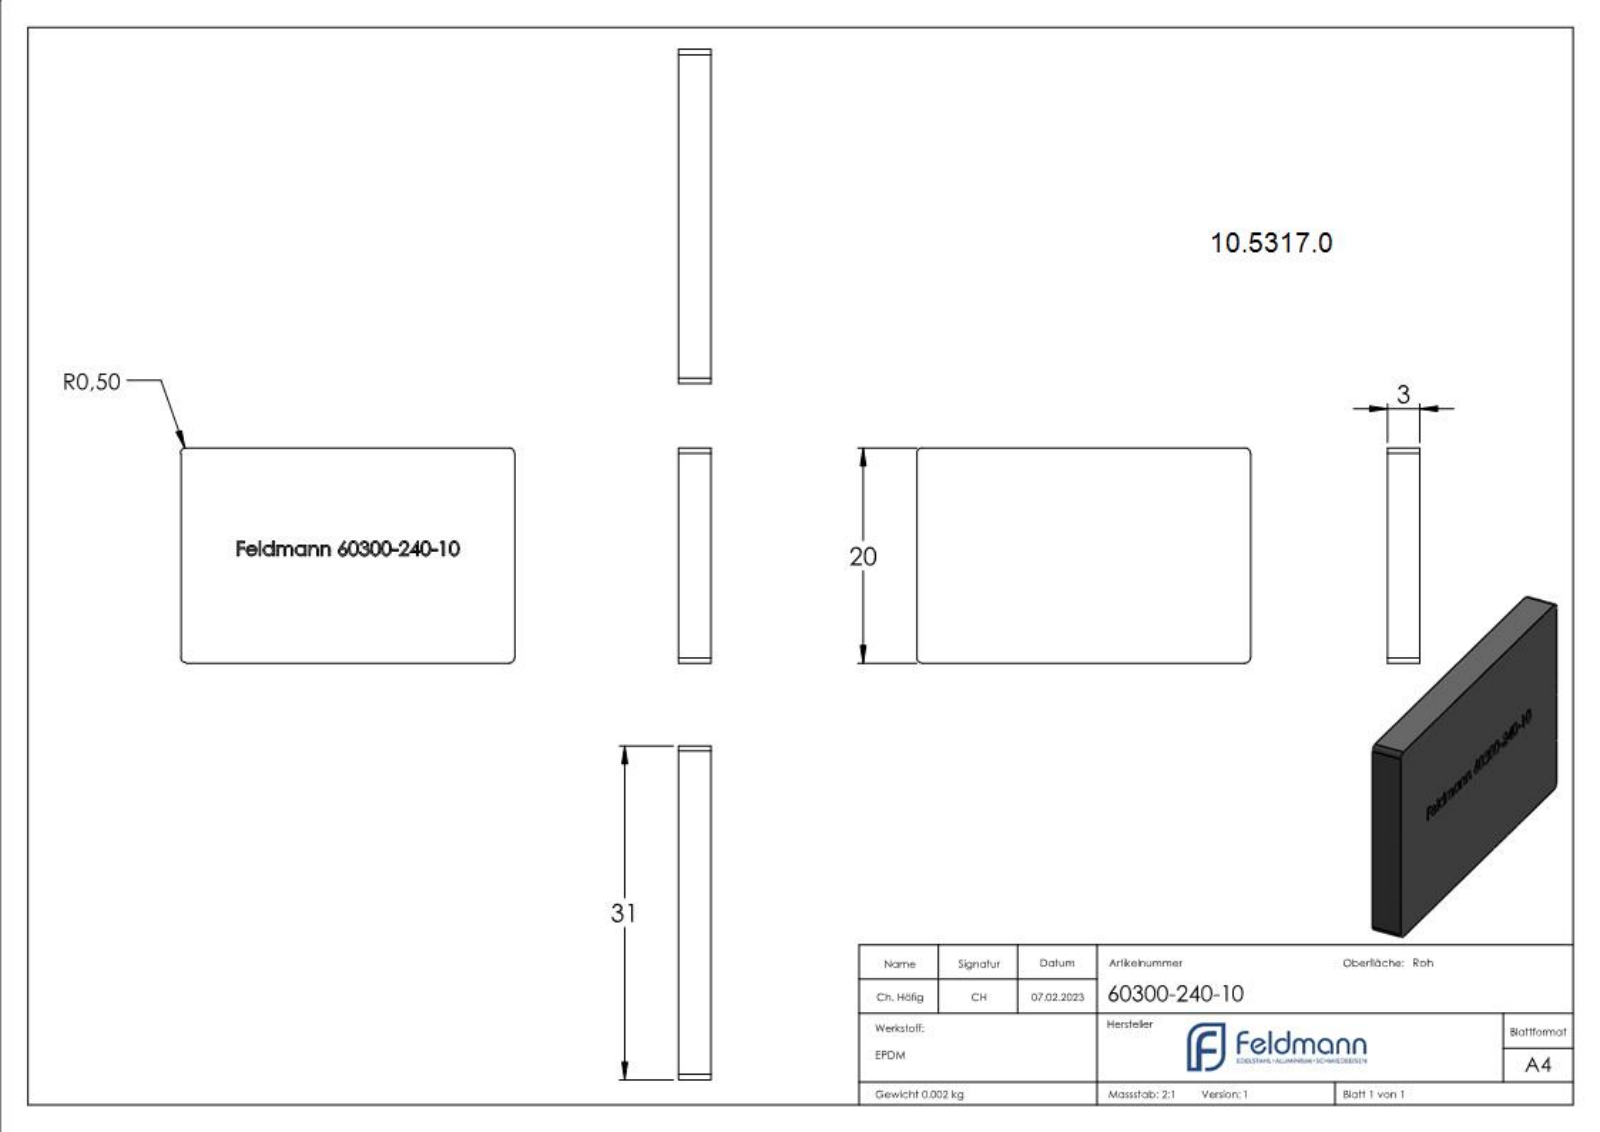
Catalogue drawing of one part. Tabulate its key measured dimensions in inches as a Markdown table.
| quantity | value |
| --- | --- |
| part name | 60300-240-10 |
| STEP written by | SolidWorks 2018 (CONFIG_CONTROL_DESIGN) |
| units | inches |
| bodies | 1 solid, 255 faces (129 planar, 4 cylindrical, 122 other) |
| overall size | 1.22 × 0.787 × 0.118 |
| volume | 0.113 in³ |
| surface area | 2.409 in² |
| partial cylindrical surfaces (radius × count) | 0.02 × 4 |
| main face-to-face distances | 0.118, 0.787, 1.22, 0.114, 0.394, 0.015, 0.671, 0.017, 0.08, 0.751 |
